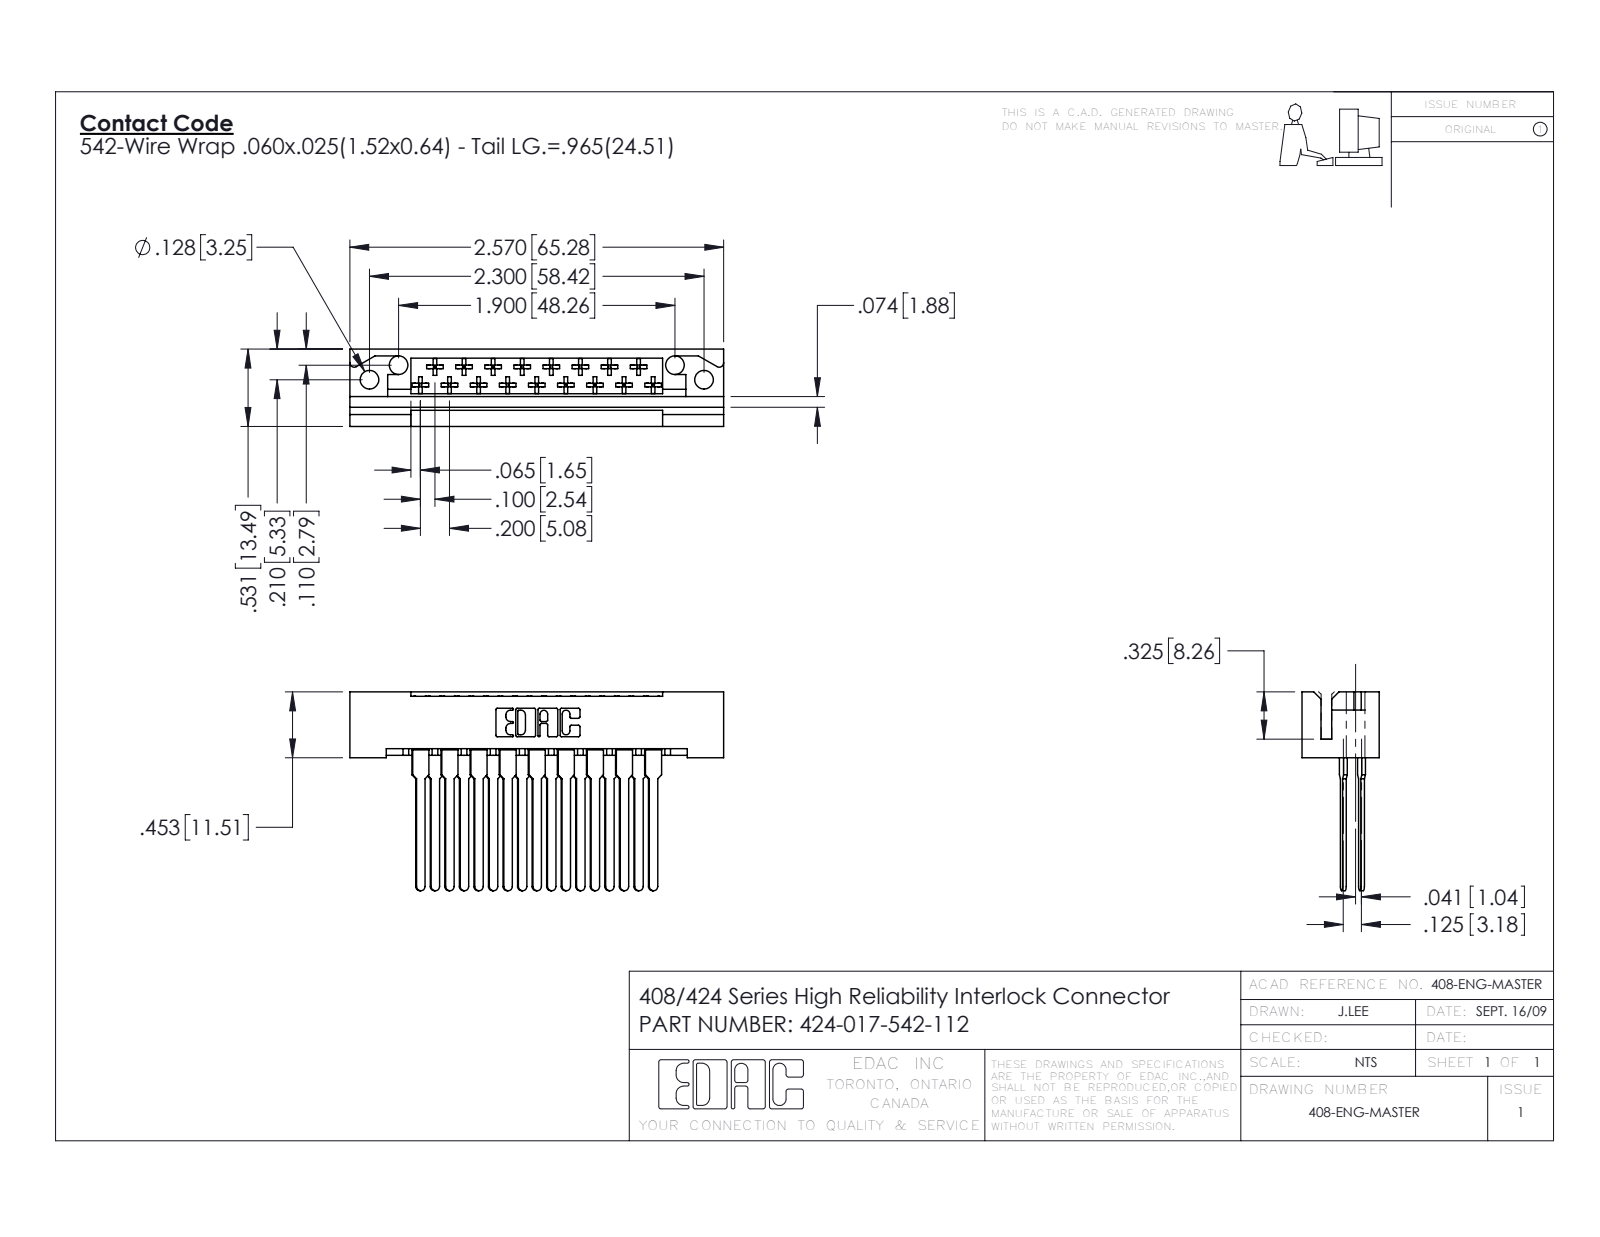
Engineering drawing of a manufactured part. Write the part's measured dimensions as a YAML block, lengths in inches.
part_name: "424-017-542-112; 408-290-001_408-290-142; 424 Part_017"
step_written_by: "SolidWorks 2016 (CONFIG_CONTROL_DESIGN)"
units: inches
bodies: {solids: 18, faces: 1046, planar: 769, cylindrical: 209, other: 68}
overall_size: [2.57, 1.367, 0.531]
volume: 0.455
surface_area: 15.44
round_holes:
  - {diameter: 0.128, count: 4}
partial_cylinders:
  - {radius: 0.01, count: 102}
  - {radius: 0.01, count: 22}
  - {radius: 0.02, count: 19}
  - {radius: 0.03, count: 19}
  - {radius: 0.007, count: 6}
  - {radius: 0.031, count: 6}
  - {radius: 0.026, count: 3}
face_to_face_distances: [0.4, 0.025, 0.531, 0.125, 0.095, 0.1, 0.131, 0.104, 0.052, 0.025]
hole_center_spacings: [0.224, 2.102, 1.9, 2.3]
